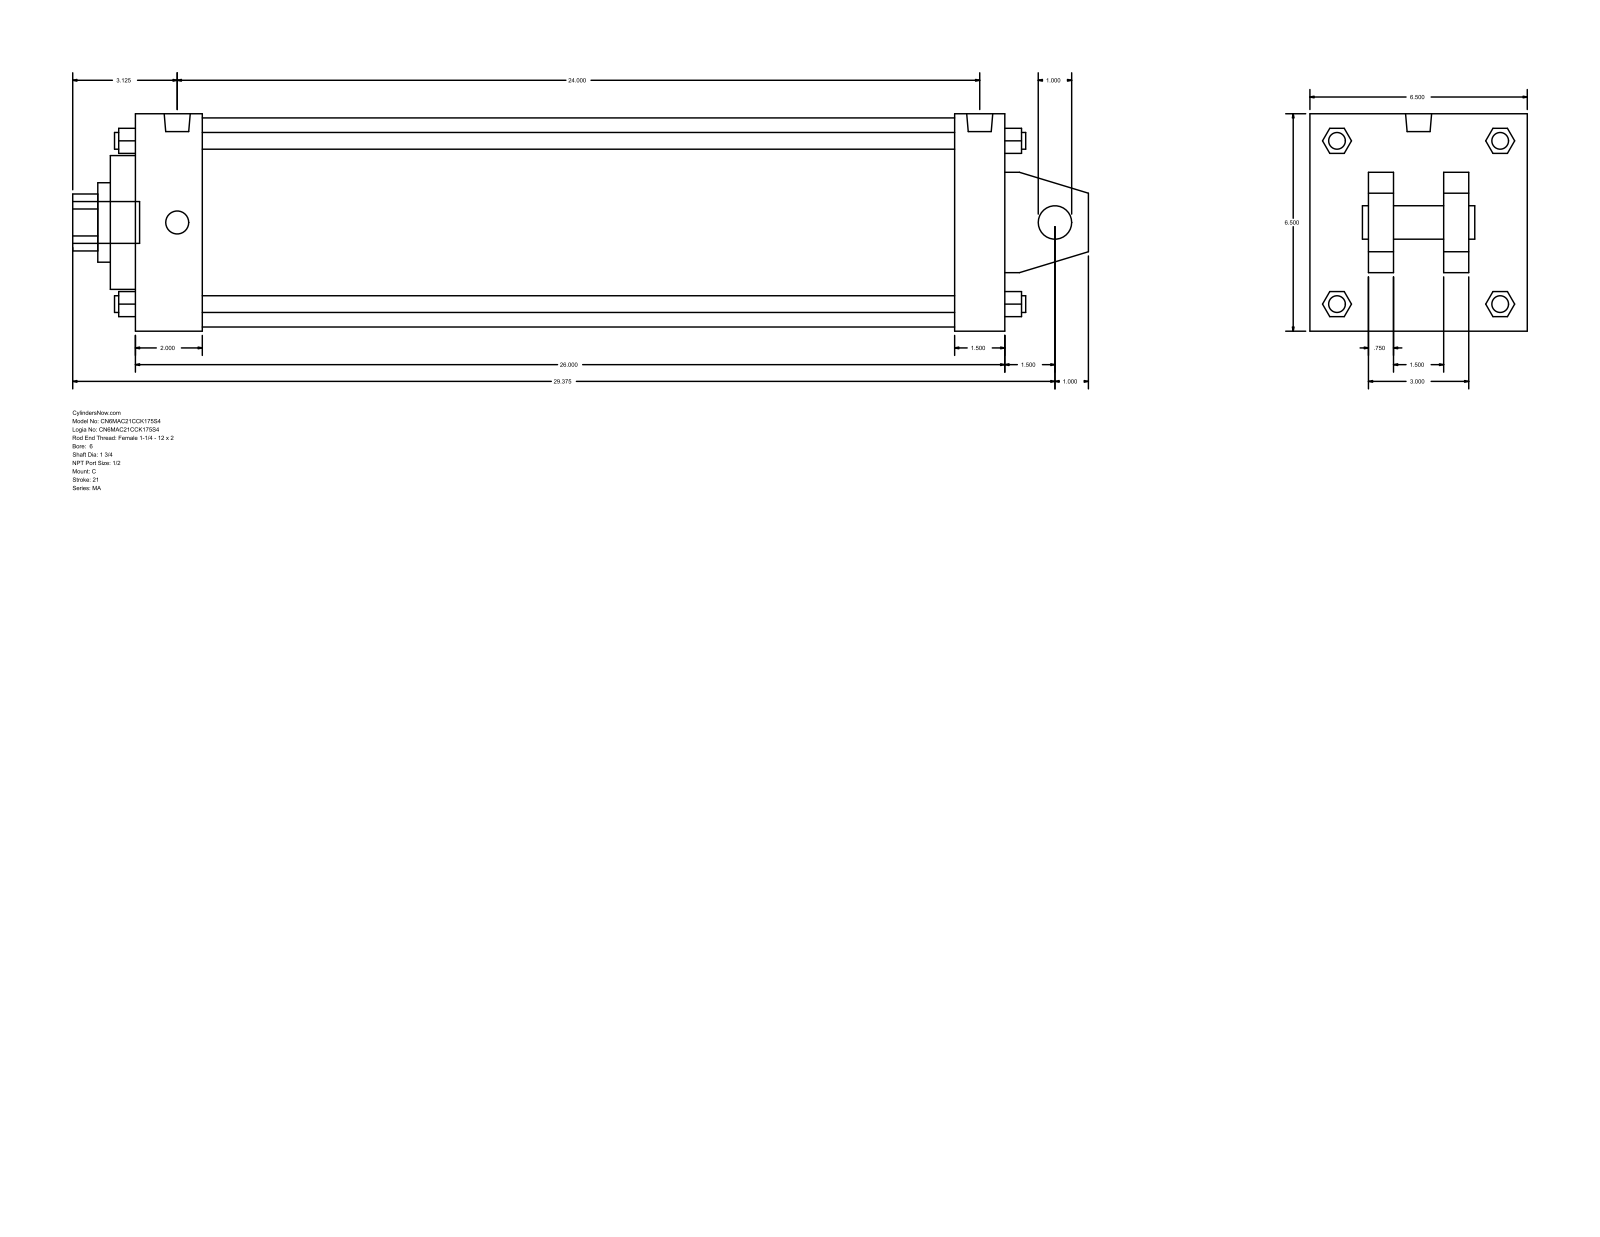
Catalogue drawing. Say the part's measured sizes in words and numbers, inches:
The part is named "MA_C__0600_1.75". Its 3-D file was written by "GSSL Pune (CONFIG_CONTROL_DESIGN)". It is 0 solids with 141 faces: 109 planar, 32 cylindrical and 0 other. Overall it measures 30.375 by 6.5 by 6.5 inches. Round holes: 1 of diameter 1, 1 of diameter 1.75, 1 of diameter 2.375, 1 of diameter 4, 1 of diameter 6.25. Round bosses or shafts: 4 of diameter 0.687, 4 of diameter 0.5, 2 of diameter 0.778, 1 of diameter 1.25. Partial cylindrical surfaces (rounded edges, fillets, slot ends): 1 of radius 0.852. The main face-to-face distances are 6.5, 26, 0.75, 1.5, 2.5, 4, 1.75, 4.75, 2.25, 2.
